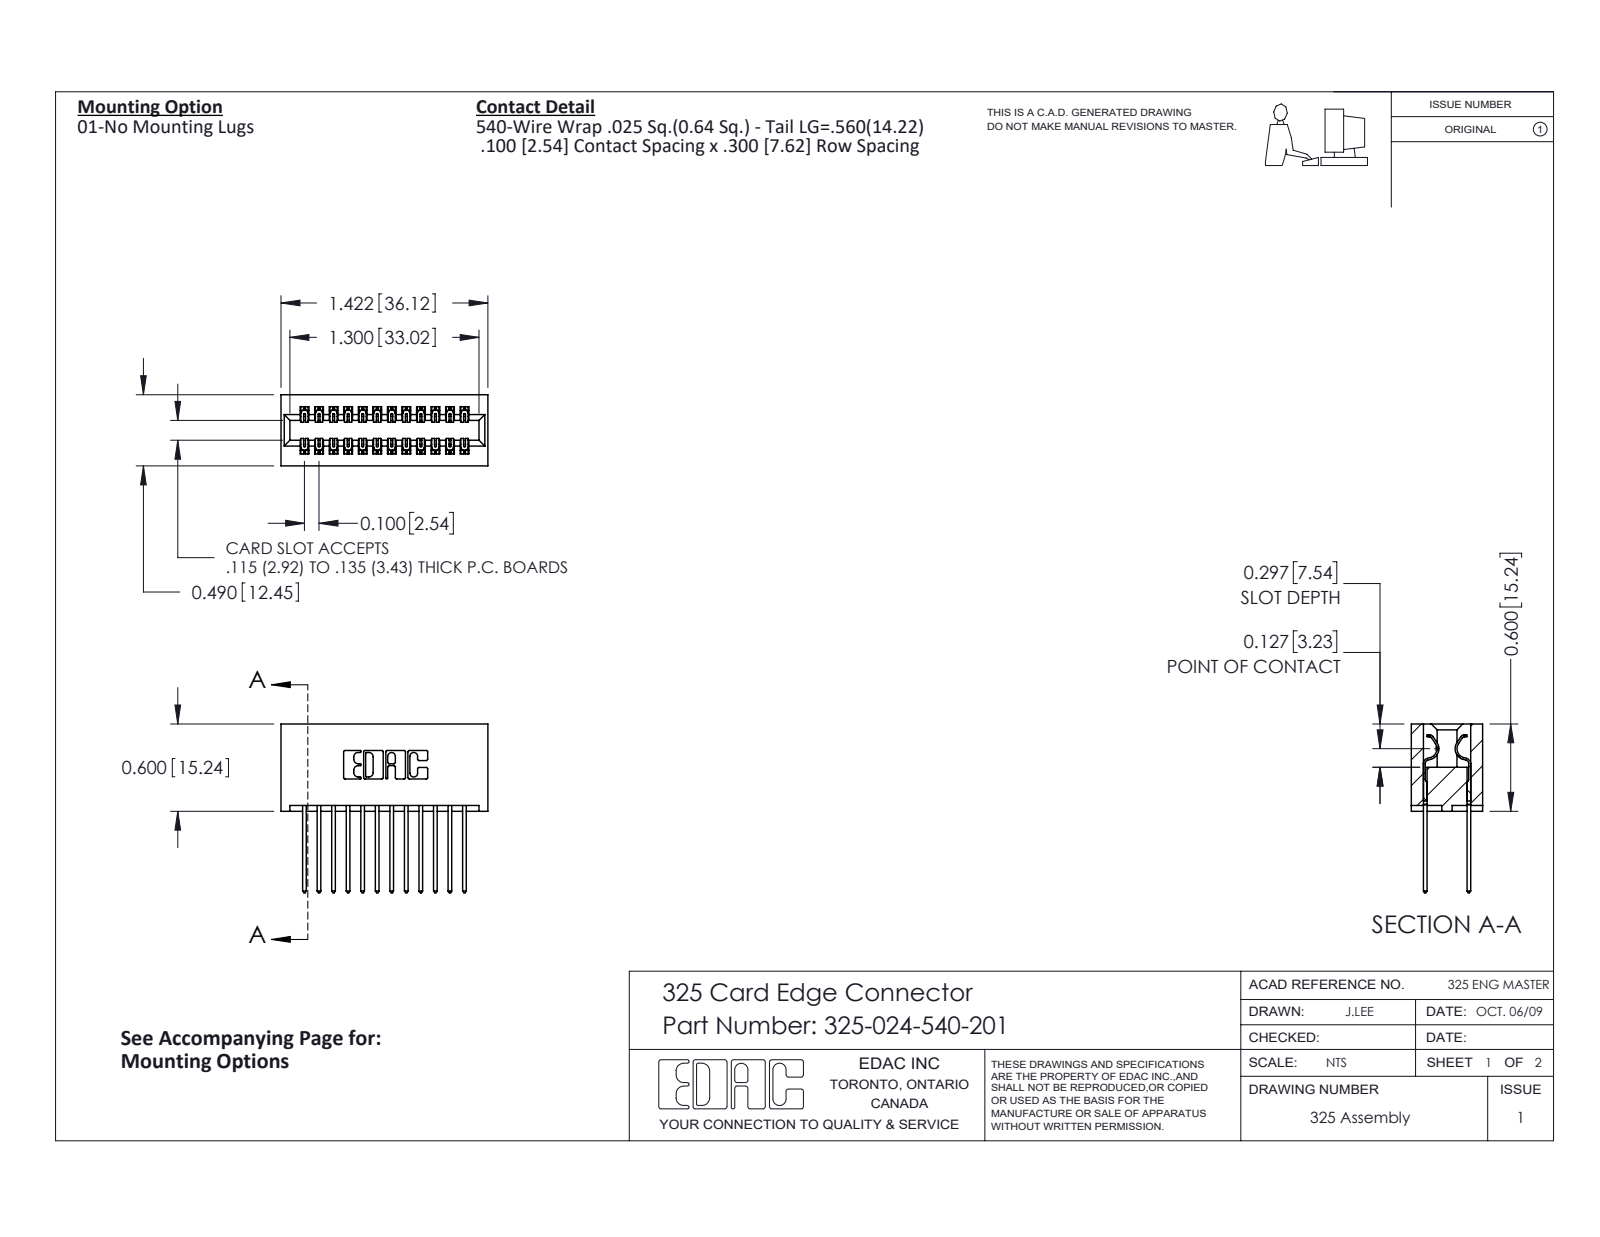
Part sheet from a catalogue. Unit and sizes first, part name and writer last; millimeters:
Units: millimetres
Overall size (bounding box): 36.1 × 29.5 × 12.4
Partial cylindrical surfaces — rounded edges, fillets, slot ends (radius × count): R0.2 ×36, R0.3 ×24, R0.3 ×22, R0.2 ×6, R0.8 ×6, R0.7 ×3, R0.4 ×2, R0.6 ×2
Main face-to-face distances: 7.6, 2.1, 10.3, 2.5, 2.7, 9.7, 0.6, 5.1, 8.3, 12.4
Volume: 5 100 mm³ · Surface area: 6 542 mm²
Bodies: 25 solids, 1354 faces (930 planar, 424 cylindrical, 0 other)
Part name (STEP PRODUCT): 325 Part_Lugless; 325-292-001_325-293-140; 325-024-540-201
STEP written by: SolidWorks 2016 (CONFIG_CONTROL_DESIGN)
